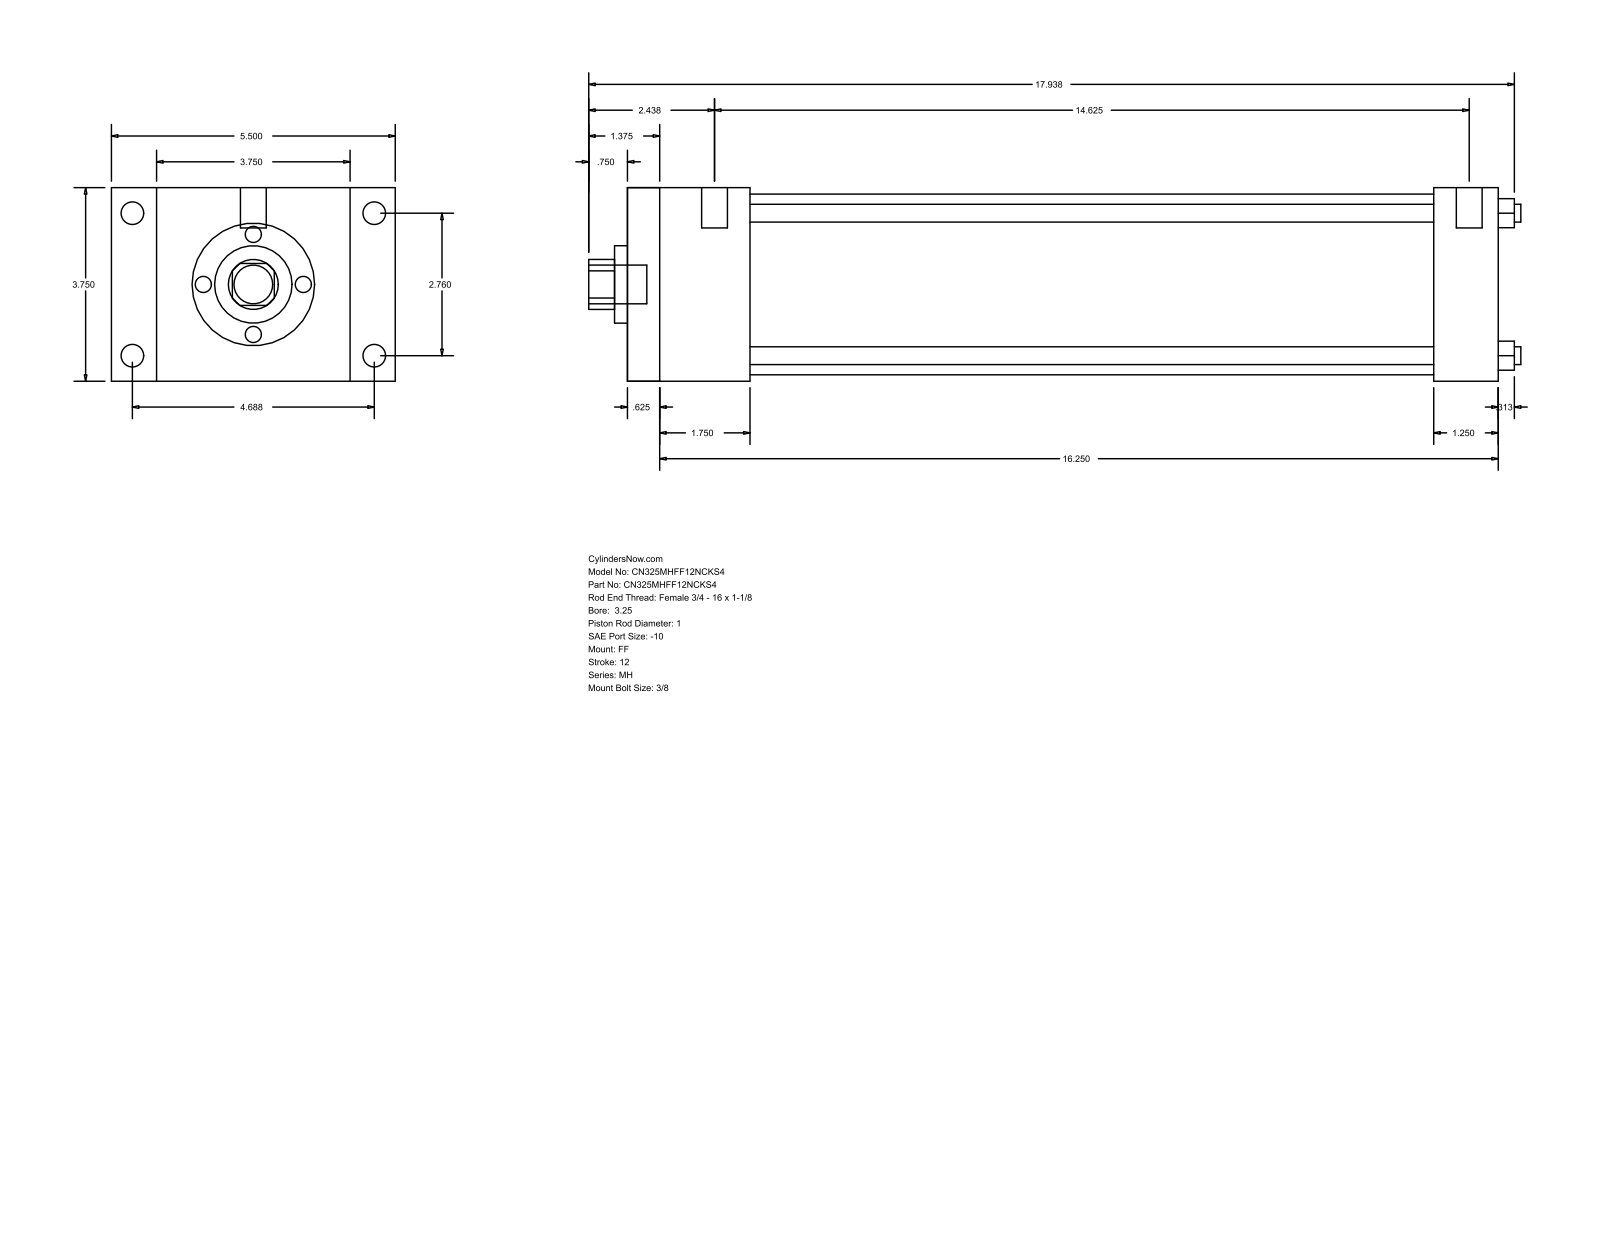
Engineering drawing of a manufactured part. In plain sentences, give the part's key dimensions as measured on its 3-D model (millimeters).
The part is named "MH_FF__0325_1". Its 3-D file was written by "GSSL Pune (CONFIG_CONTROL_DESIGN)". It is 0 solids with 92 faces: 64 planar, 28 cylindrical and 0 other. Overall it measures 458.79 by 139.7 by 95.25 millimeters. Round holes: 4 of diameter 8.76, 1 of diameter 25.4, 1 of diameter 38.1, 1 of diameter 88.9. Round bosses or shafts: 4 of diameter 11.13, 4 of diameter 5.56, 2 of diameter 12.7, 1 of diameter 19.05. Partial cylindrical surfaces (rounded edges, fillets, slot ends): 1 of radius 12.29. The main face-to-face distances are 95.24, 428.63, 15.87, 412.76, 22.23, 117.47, 396.88, 381.01, 31.75, 60.33. The hole center spacings are 49.57, 70.1, 99.14.
